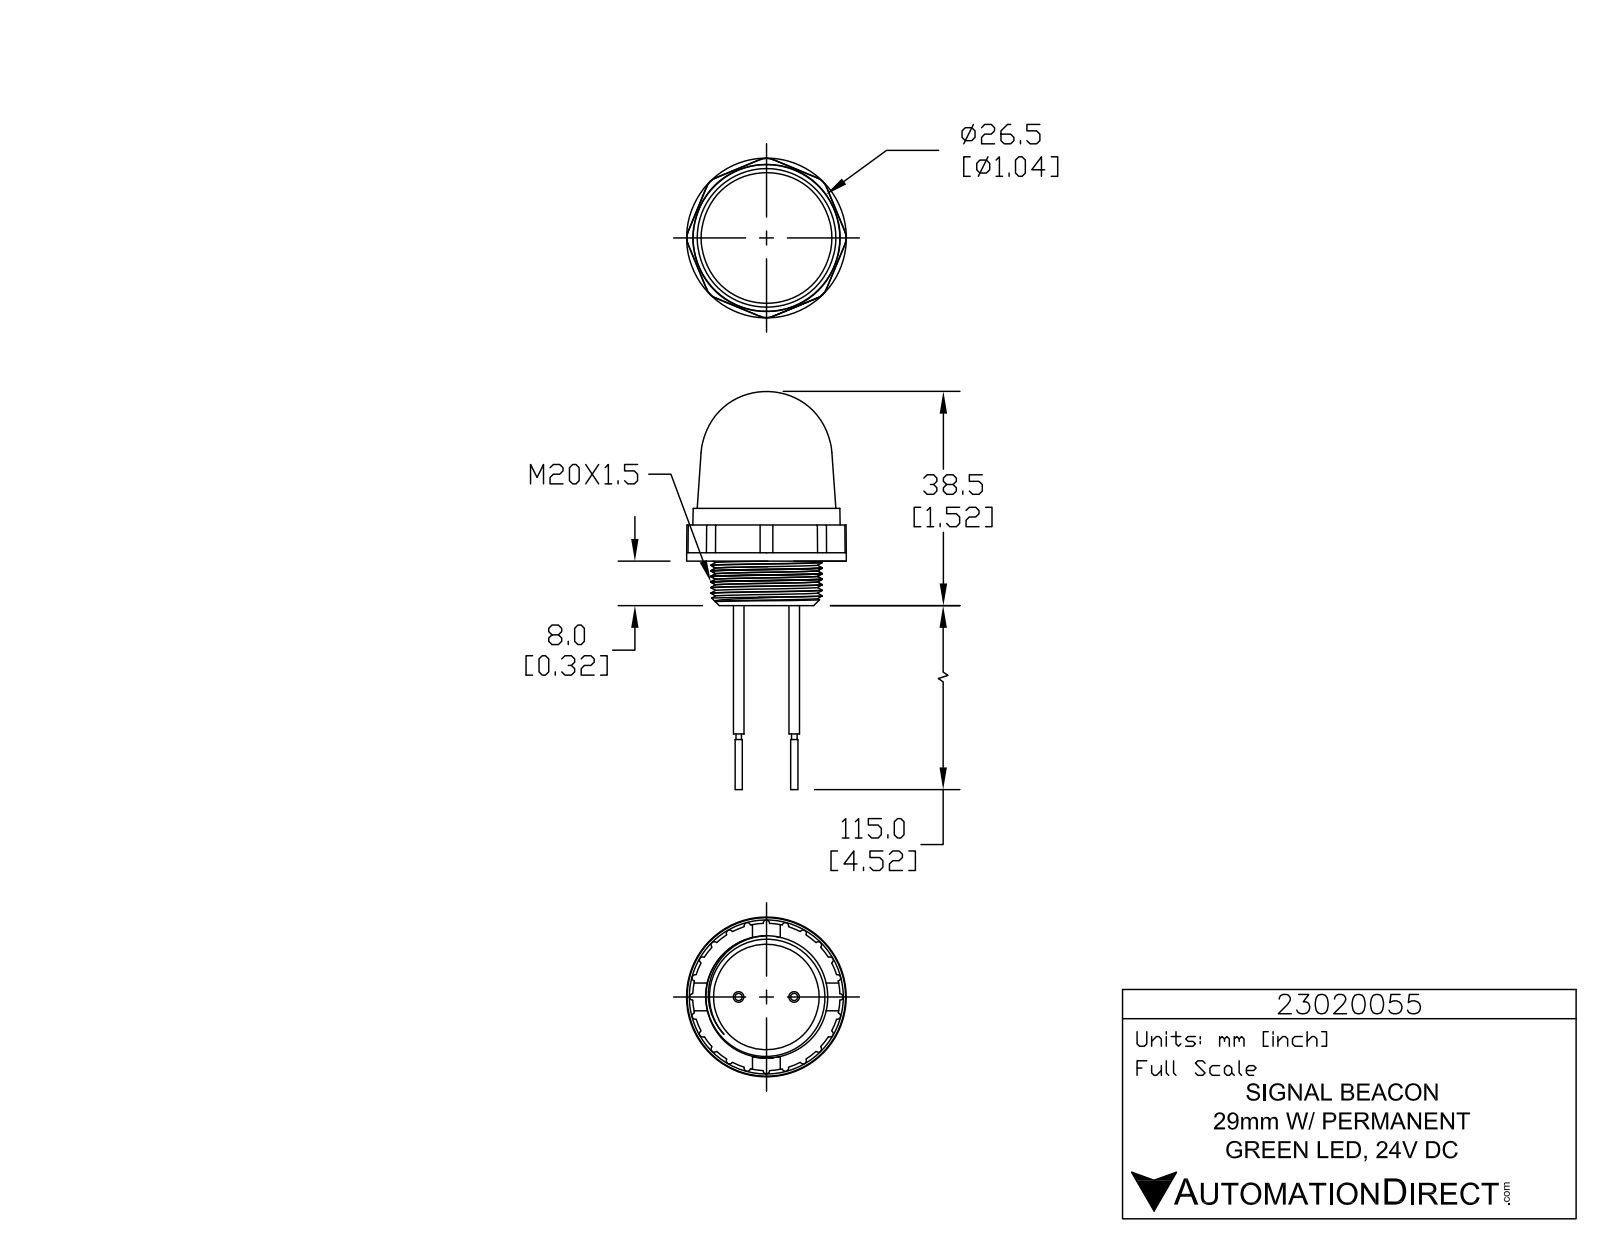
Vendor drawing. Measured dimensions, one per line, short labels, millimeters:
name: 23020055
written by: SolidWorks 2017 (AUTOMOTIVE_DESIGN)
unit: mm
bodies: 1 solid, 844 faces (551 planar, 203 cylindrical, 90 other)
size: 71.6 × 28.7 × 28.7
volume: 16 000 mm³; area: 5 263 mm²
holes: 3× ⌀0.5, 1× ⌀20.5
bosses: 3× ⌀2.9, 3× ⌀0.7, 2× ⌀1.9, 2× ⌀1.3, 2× ⌀1, 1× ⌀28.7, 1× ⌀28.5, 1× ⌀22.7
rounds: 8× R3, 6× R0.1, 6× R0.1, 6× R0.1, 6× R1.7, 3× R0.1, 3× R0.2, 3× R0.2
face distances: 7, 9.5, 1, 8, 16.5, 16.2, 9.2, 17.5, 10.5, 1.3
